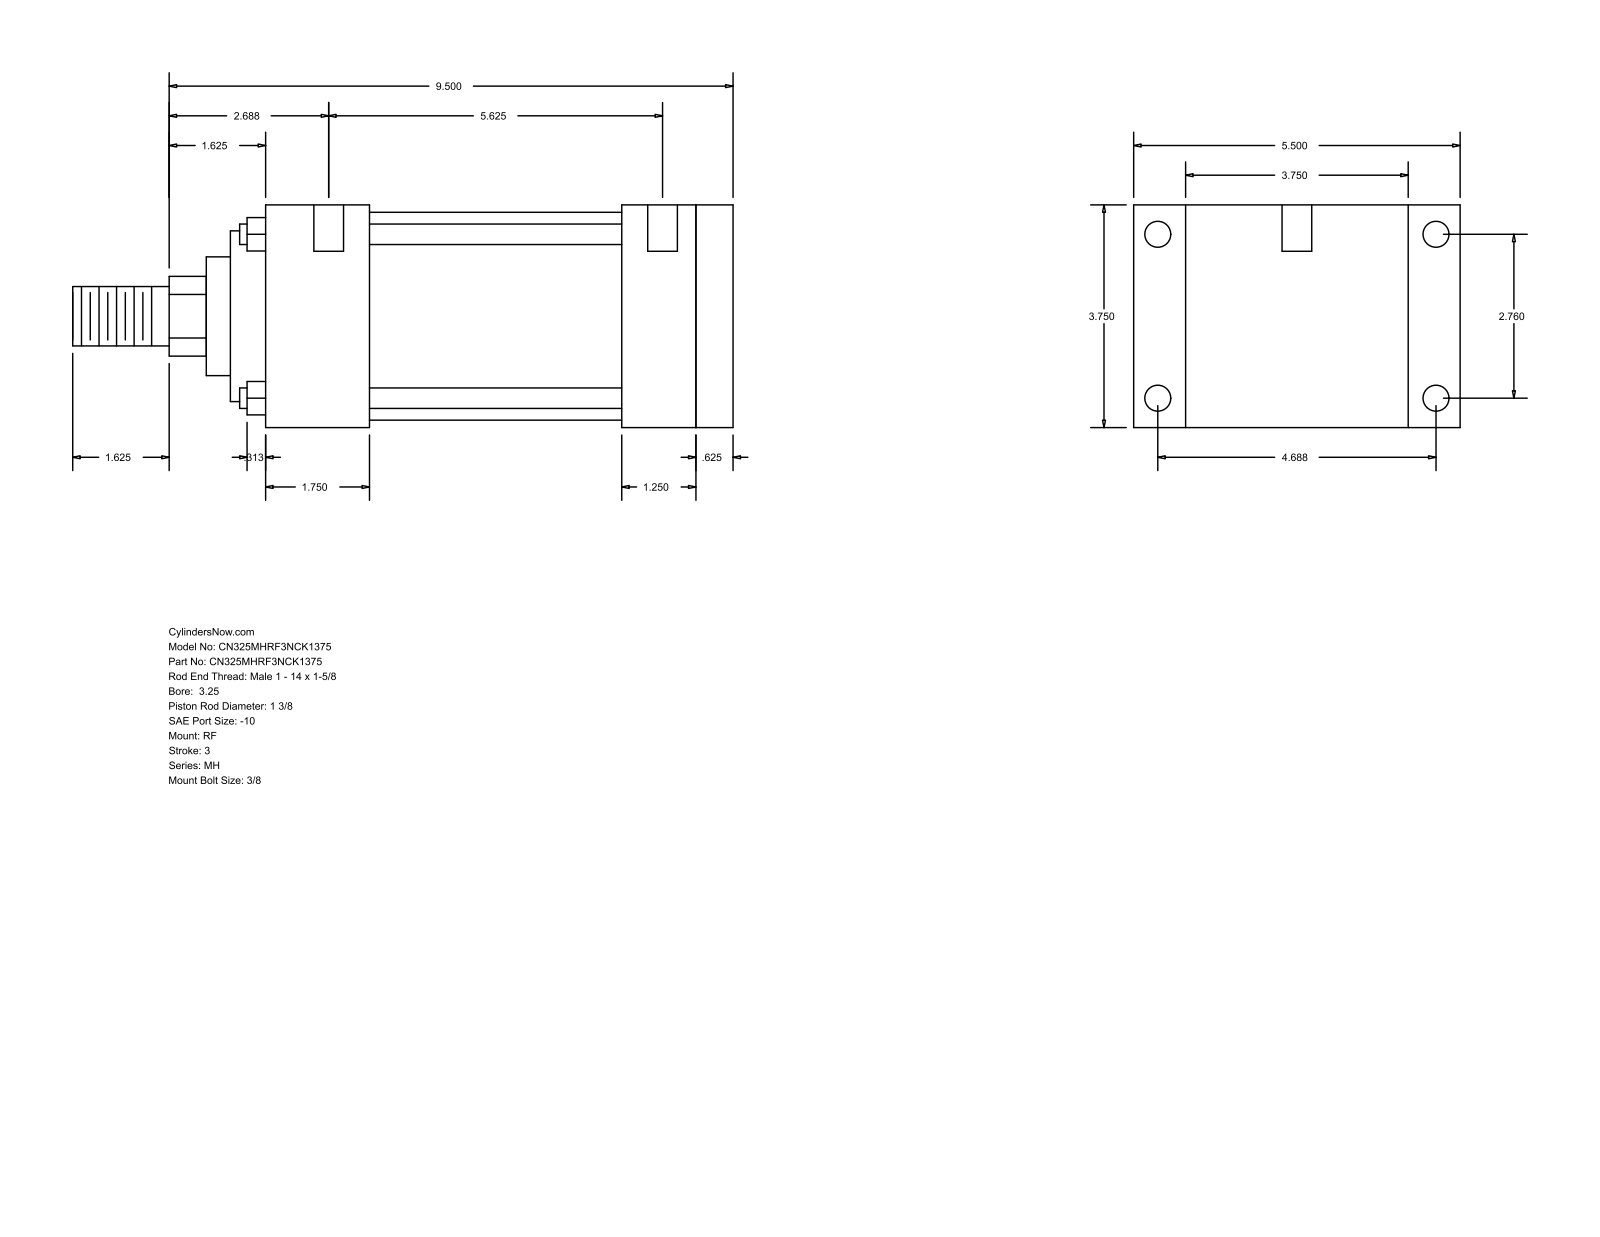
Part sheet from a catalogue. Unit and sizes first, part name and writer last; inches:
Units: inches
Overall size (bounding box): 11.125 × 5.5 × 3.75
Round holes (diameter × count): ⌀0.219 ×4, ⌀0.438 ×4, ⌀0.5 ×2
Round bosses / shafts (diameter × count): ⌀0.345 ×4, ⌀3.5 ×1, ⌀2.875 ×1, ⌀2 ×1, ⌀1.375 ×1, ⌀1 ×1
Partial cylindrical surfaces — rounded edges, fillets, slot ends (radius × count): R0.672 ×1
Main face-to-face distances: 3.75, 7.875, 7.25, 0.625, 0.875, 4.625, 1.75, 5.5, 6.125, 6
Hole centre spacings: 2.76, 4.687, 5.439, 5.875, 0.063, 0.187, 5.625, 5.688
Bodies: 0 solids, 94 faces (65 planar, 29 cylindrical, 0 other)
Part name (STEP PRODUCT): MH_RF__0325_1.375
STEP written by: GSSL Pune (CONFIG_CONTROL_DESIGN)
